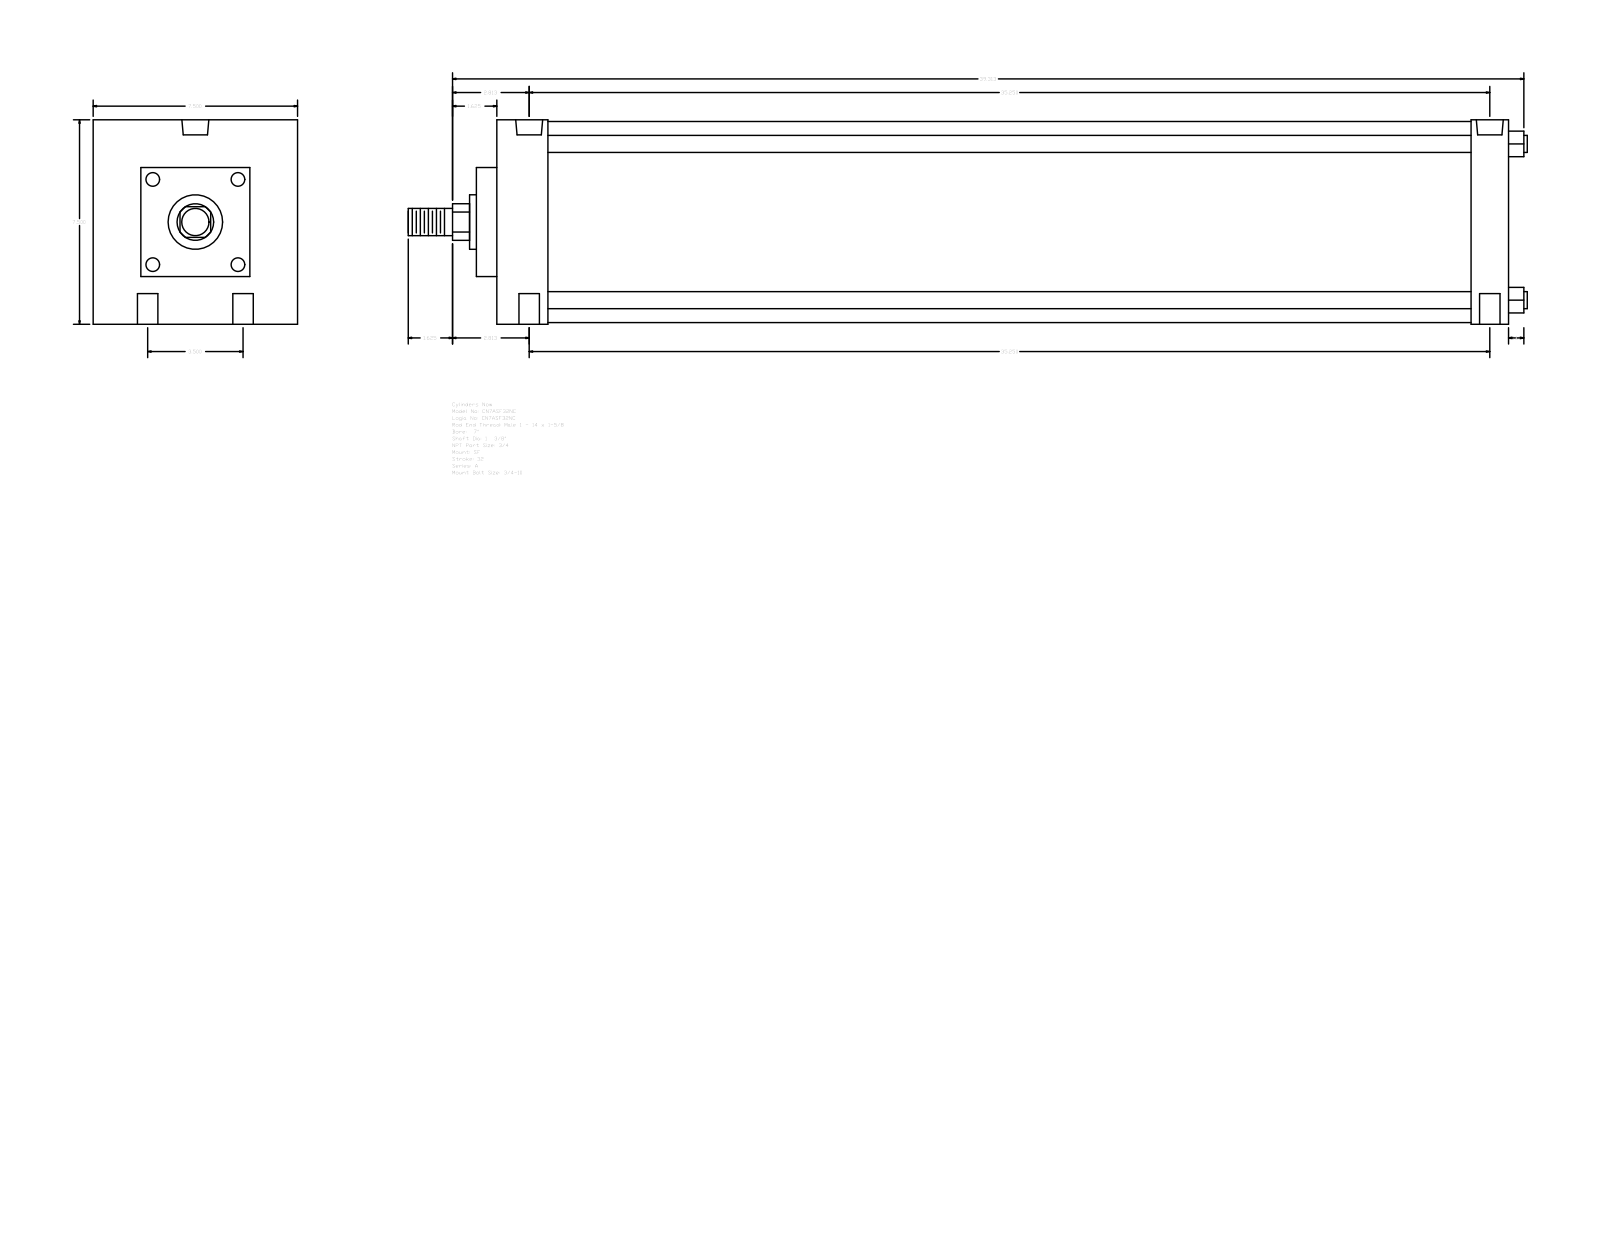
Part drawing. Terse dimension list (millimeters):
name: A_SF__0700_1.375
written by: GSSL Pune (CONFIG_CONTROL_DESIGN)
unit: mm
bodies: 0 solids, 93 faces (67 planar, 26 cylindrical, 0 other)
size: 1042.99 × 190.5 × 190.5
holes: 4× ⌀19.05, 2× ⌀15.08, 2× ⌀25.12
bosses: 4× ⌀15.88, 1× ⌀187.32, 1× ⌀50.8, 1× ⌀34.92, 1× ⌀25.4
rounds: 1× R17.06
face distances: 190.5, 942.98, 19.04, 962.02, 66.67, 927.1, 47.63, 908.06, 860.43, 895.35
hole spacings: 44.45, 896.45, 895.35, 88.9, 899.75, 884.23
